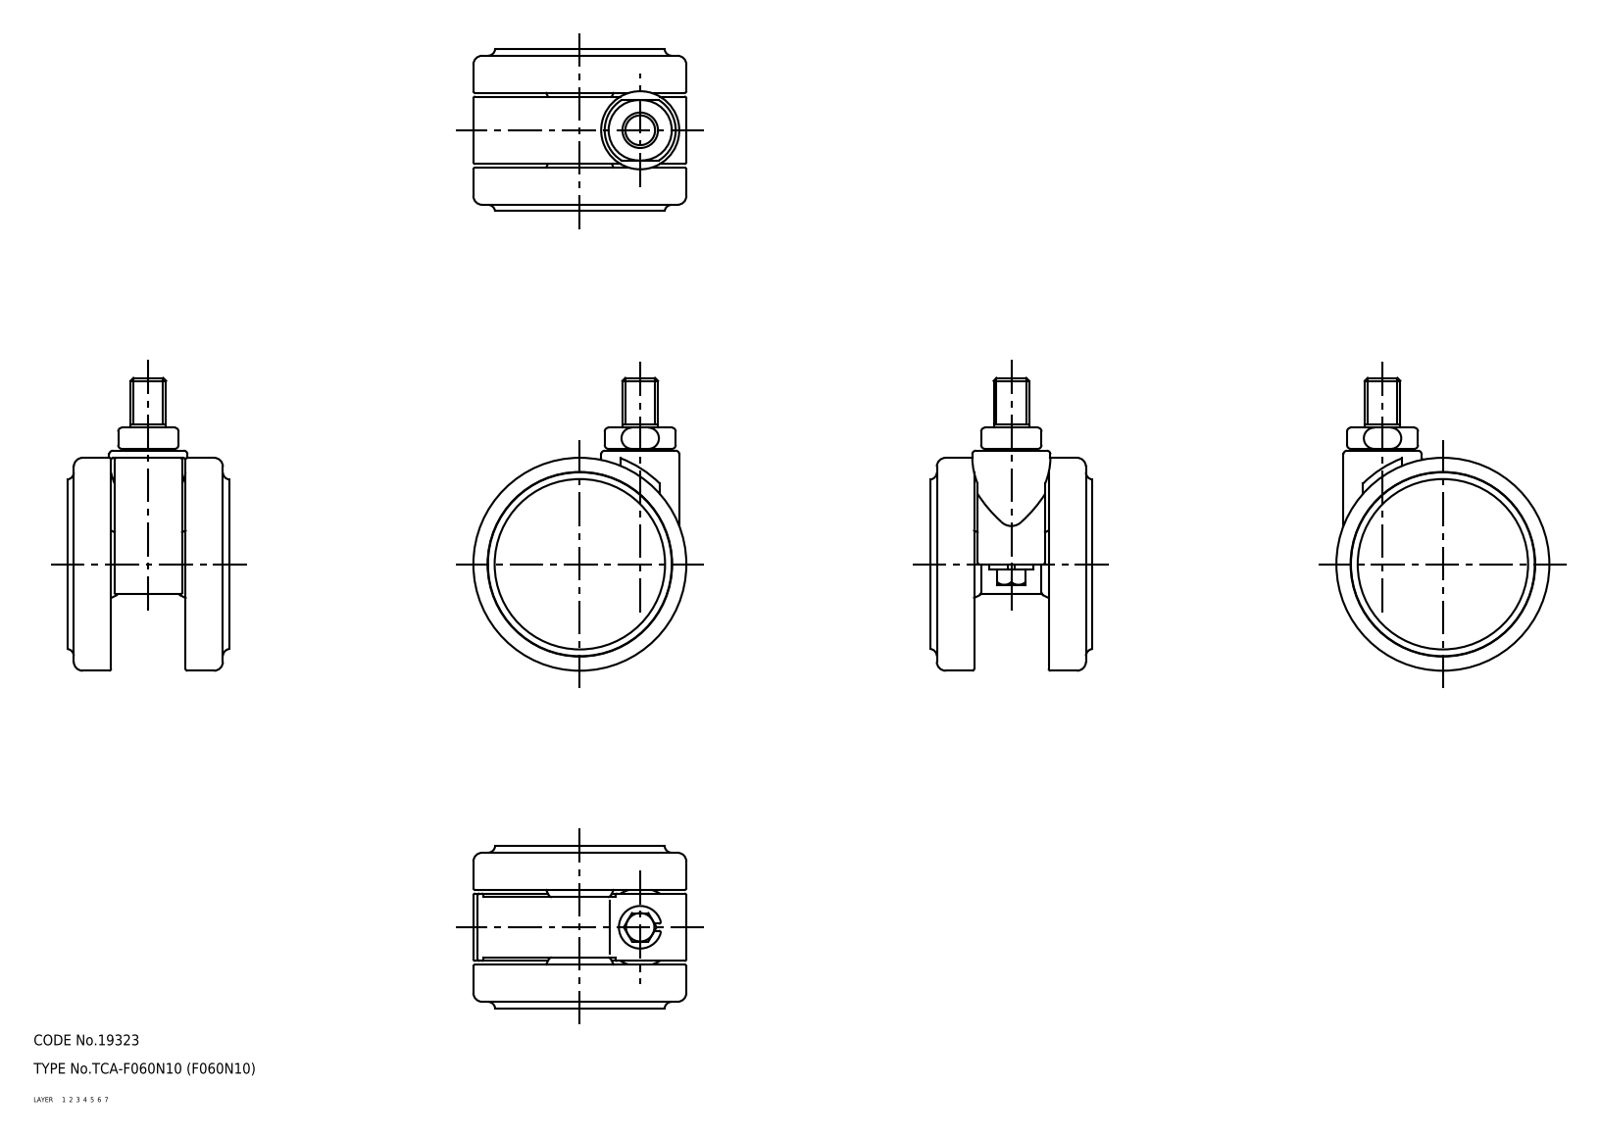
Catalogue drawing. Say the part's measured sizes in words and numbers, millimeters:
The part is named "67118946; 67118959; 67118972; 67118985". Its 3-D file was written by "CADfix (AUTOMOTIVE_DESIGN)". It is 4 solids with 150 faces: 0 planar, 0 cylindrical and 150 other. Overall it measures 82.5 by 60 by 45.6 millimeters. Its volume is 86 305 cubic millimeters and its surface area 27 447 square millimeters.
